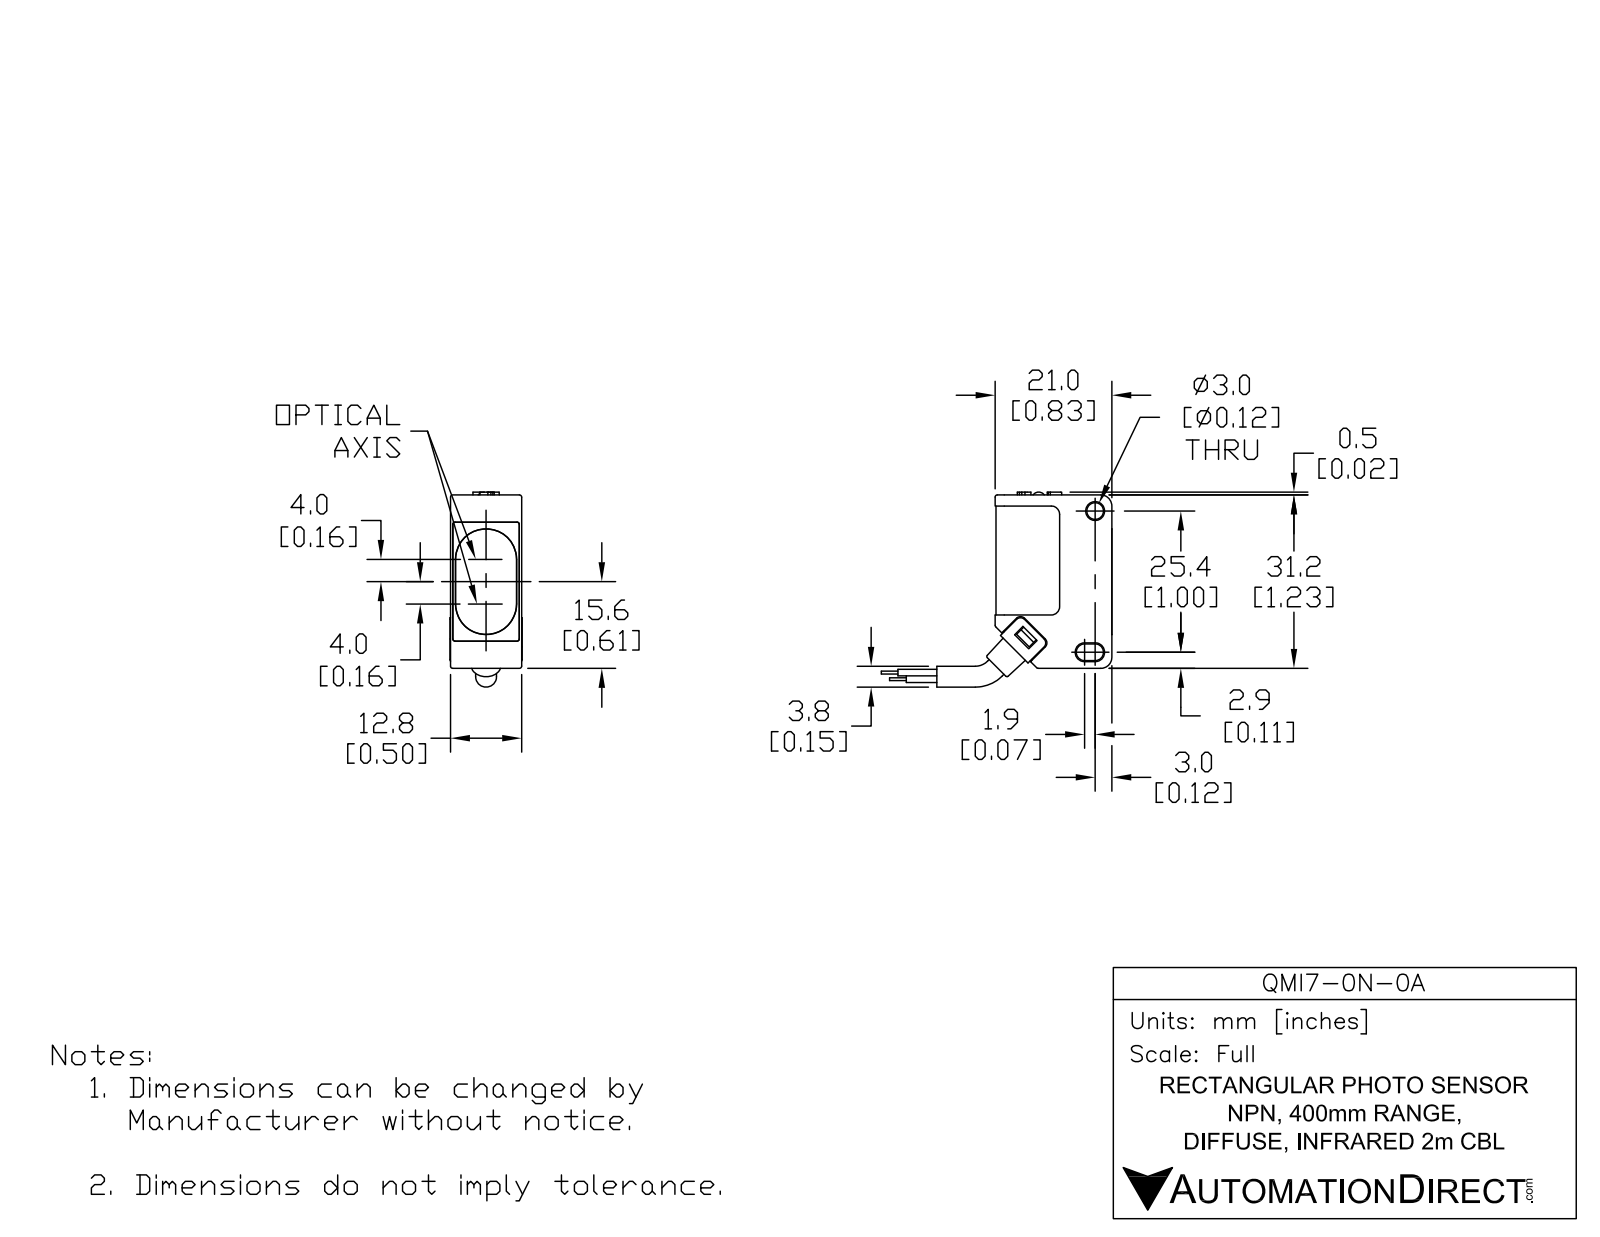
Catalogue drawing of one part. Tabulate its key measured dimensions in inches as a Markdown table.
| quantity | value |
| --- | --- |
| part name | QMI7-0N-0A |
| STEP written by | SolidWorks 2017 (AUTOMOTIVE_DESIGN) |
| units | inches |
| bodies | 9 solids, 258 faces (134 planar, 100 cylindrical, 24 other) |
| overall size | 3.193 × 1.032 × 0.512 |
| volume | 0.47 in³ |
| surface area | 8.375 in² |
| round holes (diameter × count) | 0.118 × 3, 0.148 × 1, 0.224 × 1, 0.283 × 1 |
| round bosses / shafts (diameter × count) | 0.138 × 2 |
| partial cylindrical surfaces (radius × count) | 0.016 × 13, 0.02 × 10, 0.039 × 8, 0.059 × 6, 0.024 × 4, 0.006 × 2, 0.035 × 2, 0.044 × 2 |
| main face-to-face distances | 0.02, 0.498, 0.059, 0.016, 0.504, 0.138, 0.488, 0.079, 0.482, 0.492 |
| hole center spacings | 0.205 |
